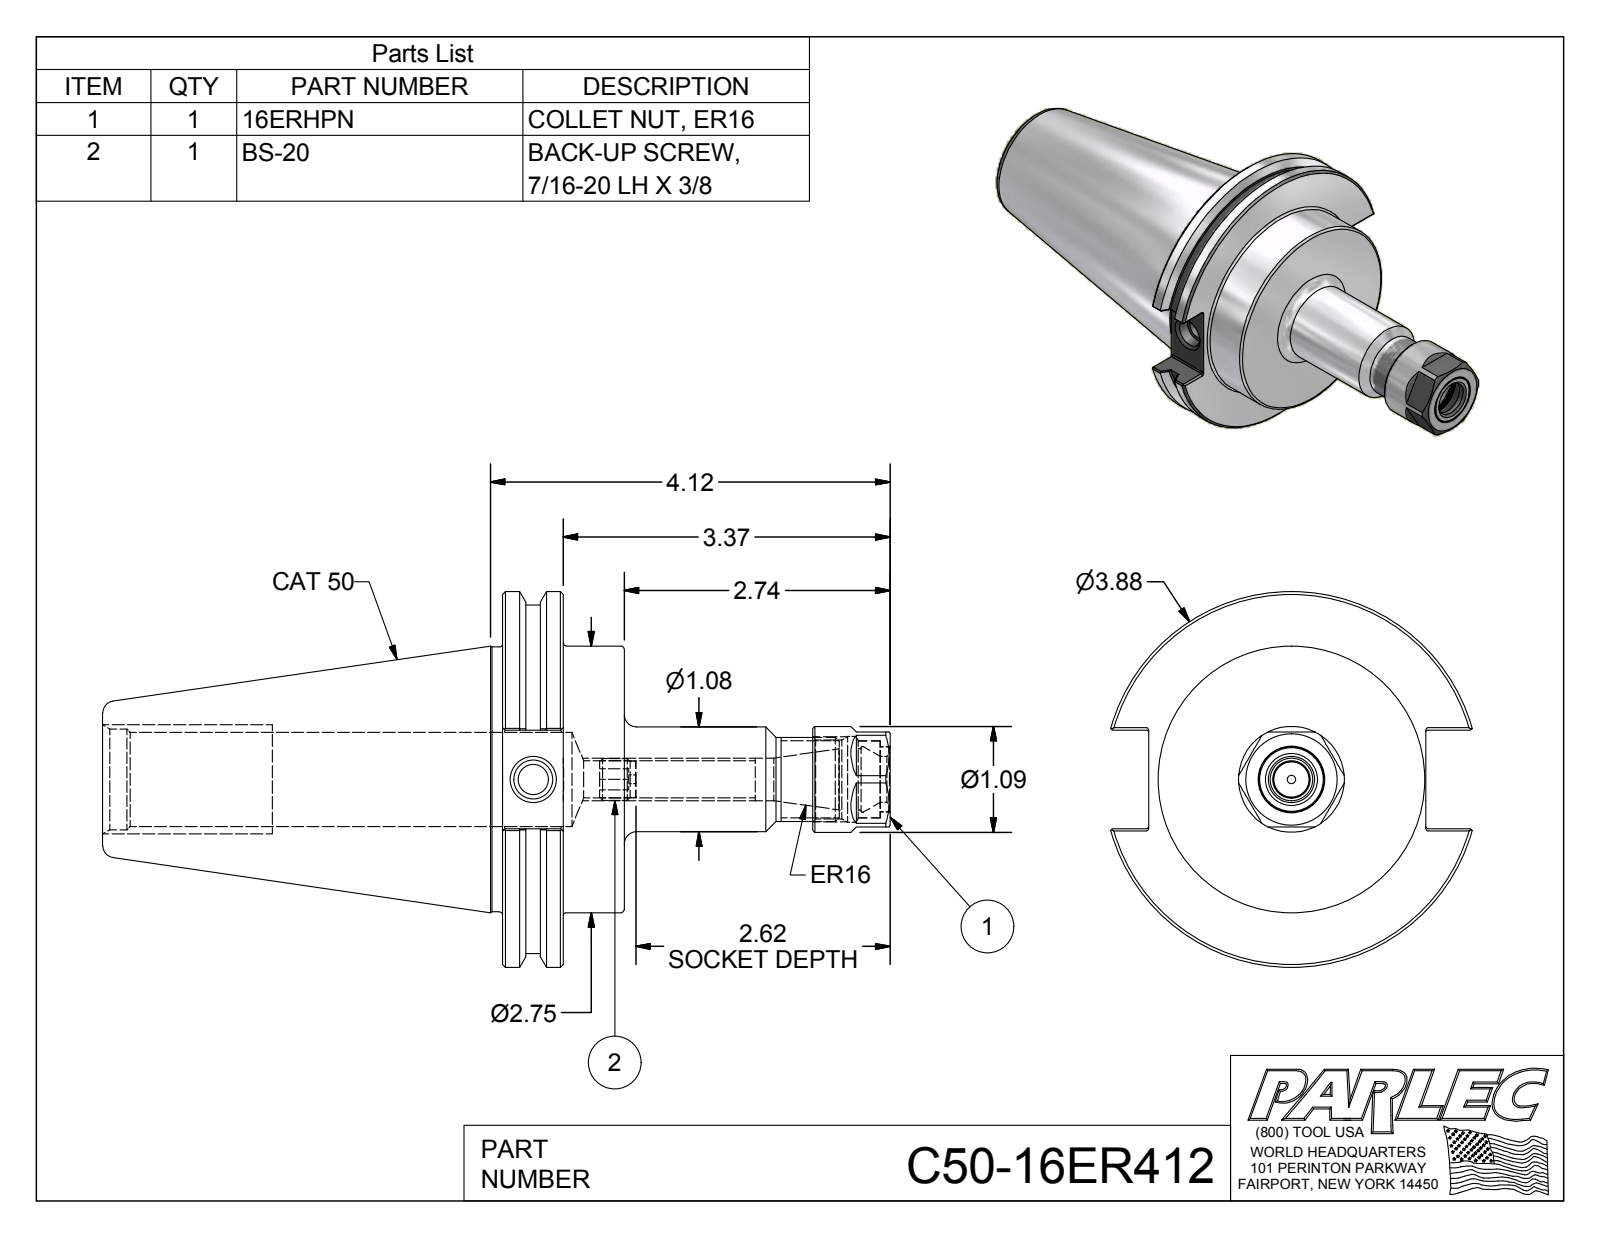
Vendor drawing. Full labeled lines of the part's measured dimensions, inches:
Part name (STEP PRODUCT): C50-16ER412; C50-16ER4-1; 16ERHPN; BS-20
STEP written by: Autodesk Inventor 2012 (AUTOMOTIVE_DESIGN)
Units: inches
Bodies: 4 solids, 151 faces (62 planar, 41 cylindrical, 48 other)
Overall size (bounding box): 8.12 × 3.875 × 3.729
Volume: 24.15 in³ · Surface area: 94.64 in²
Round holes (diameter × count): ⌀0.09 ×1, ⌀0.315 ×1, ⌀0.383 ×1, ⌀0.399 ×1, ⌀0.44 ×1, ⌀0.474 ×1, ⌀0.63 ×1, ⌀0.674 ×1, ⌀0.68 ×1, ⌀0.794 ×1, ⌀0.814 ×1, ⌀0.883 ×1
Round bosses / shafts (diameter × count): ⌀3.875 ×1, ⌀3.594 ×1, ⌀2.75 ×1, ⌀2.73 ×1, ⌀1.092 ×1, ⌀1.08 ×1, ⌀0.866 ×1, ⌀0.79 ×1
Partial cylindrical surfaces — rounded edges, fillets, slot ends (radius × count): R0.02 ×12
Main face-to-face distances: 1.255, 0.625, 0.63, 4.125, 4.75, 5.38, 0.98, 8.12, 3.995, 3.37
